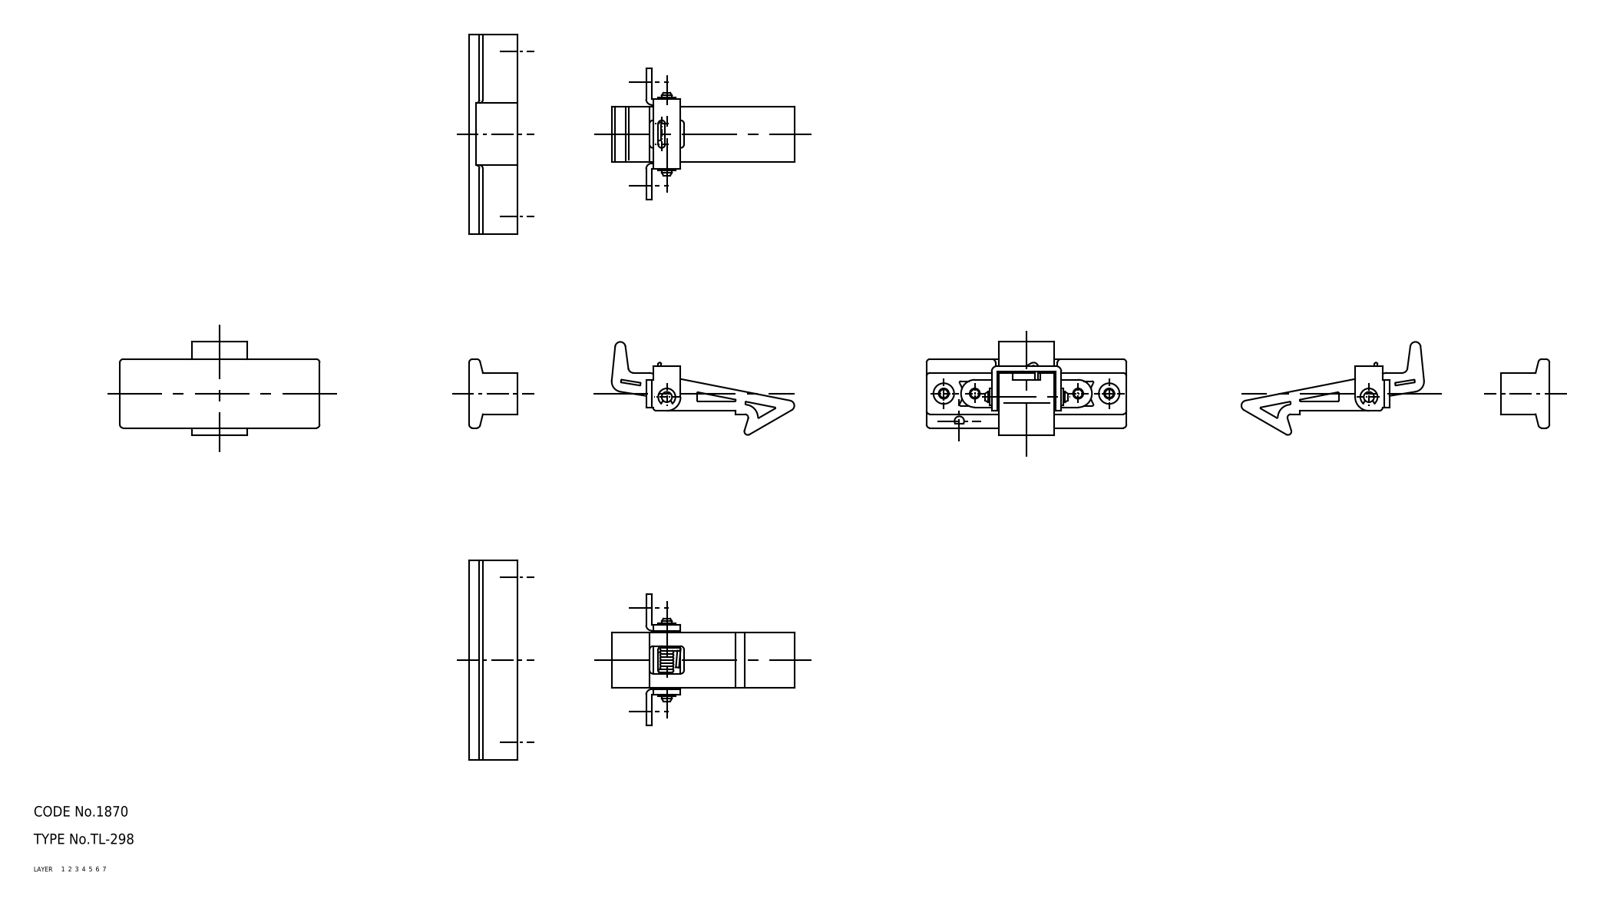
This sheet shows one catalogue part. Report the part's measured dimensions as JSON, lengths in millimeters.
{"part_name": "67122771; 67122784; 67122797; 67122810 (+3 more)", "step_written_by": "CADfix (AUTOMOTIVE_DESIGN)", "units": "millimeters", "bodies": {"solids": 7, "faces": 270, "planar": 0, "cylindrical": 0, "other": 270}, "overall_size": [59.6, 58, 27], "volume_mm3": 14407, "surface_area_mm2": 10600}
